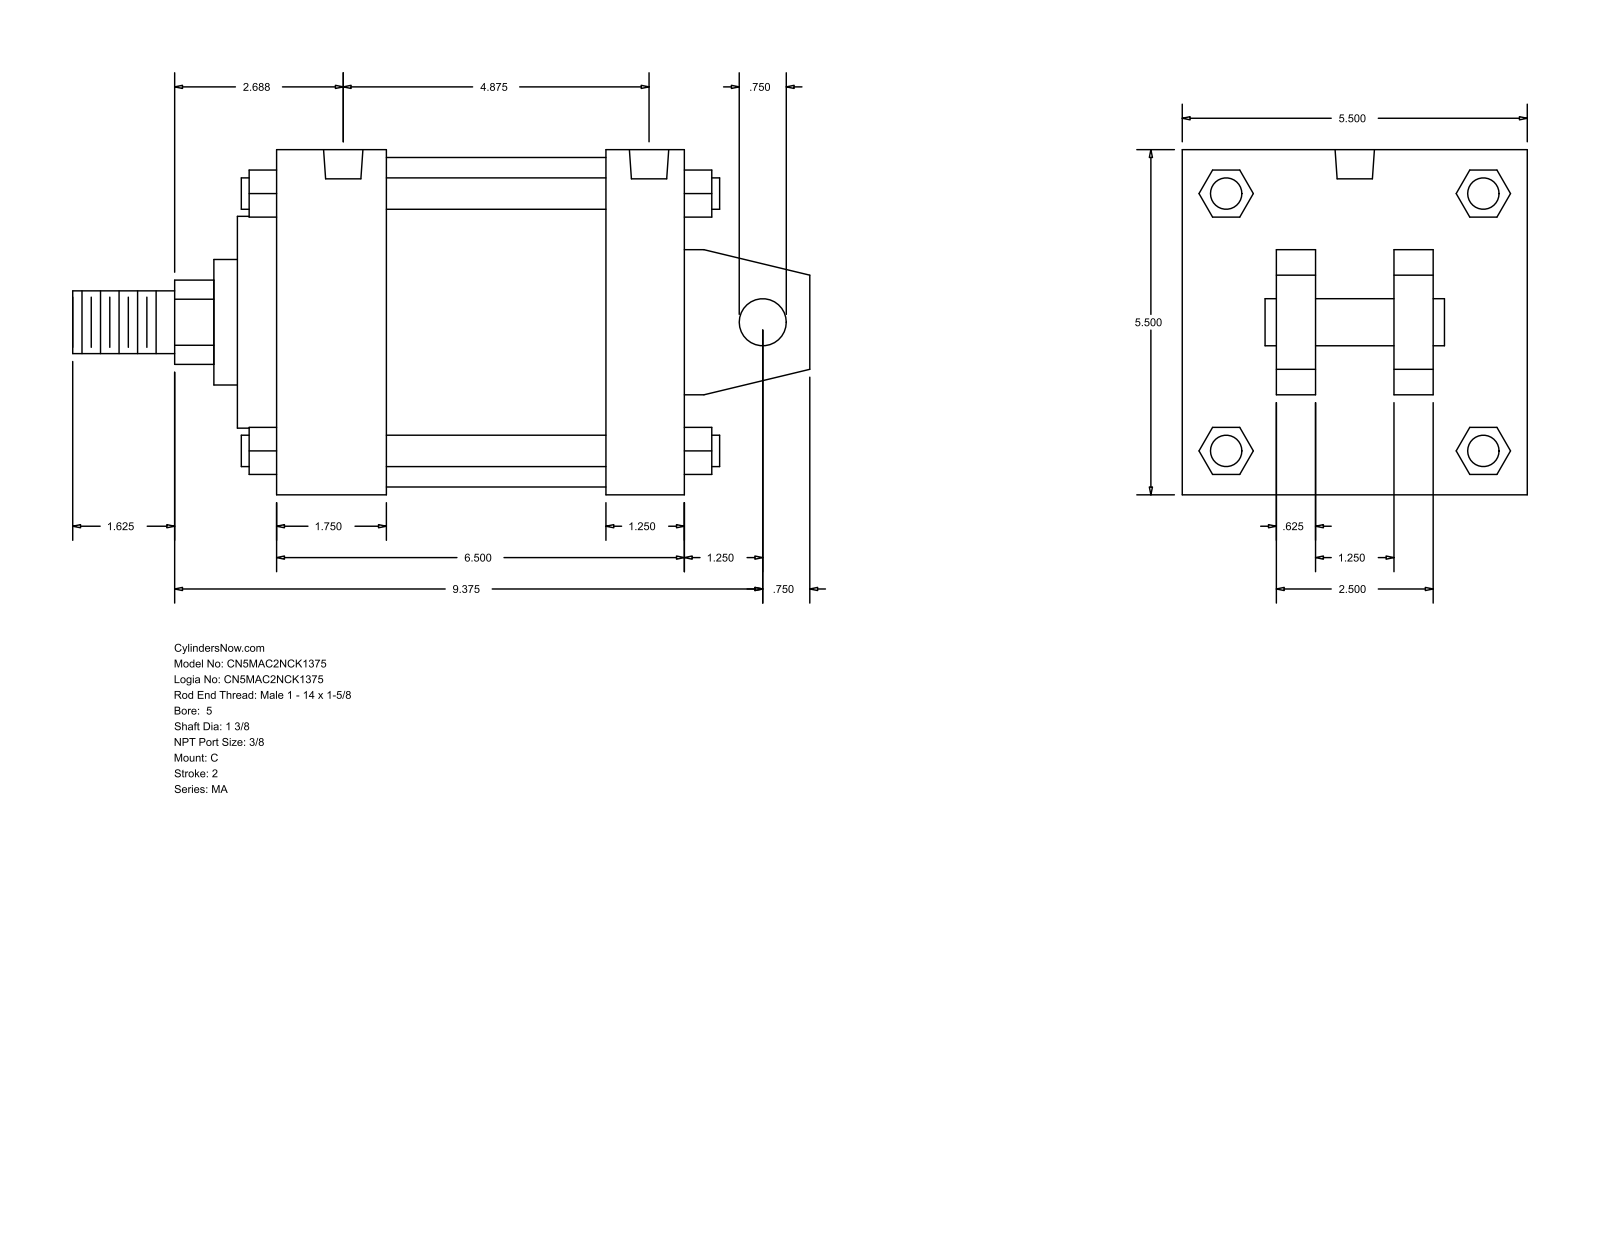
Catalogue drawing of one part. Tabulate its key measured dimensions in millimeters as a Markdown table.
| quantity | value |
| --- | --- |
| part name | MA_C__0500_1.375 |
| STEP written by | GSSL Pune (CONFIG_CONTROL_DESIGN) |
| units | millimeters |
| bodies | 0 solids, 141 faces (109 planar, 32 cylindrical, 0 other) |
| overall size | 298.45 × 139.7 × 139.7 |
| round holes (diameter × count) | 11.11 × 4, 15.93 × 2 |
| round bosses / shafts (diameter × count) | 12.7 × 4, 133.35 × 1, 85.72 × 1, 50.8 × 1, 34.92 × 1, 25.4 × 1, 19.05 × 1 |
| partial cylindrical surfaces (radius × count) | 17.06 × 1 |
| main face-to-face distances | 139.7, 165.11, 15.87, 31.76, 133.35, 44.45, 88.9, 120.66, 53.97, 38.1 |
| hole center spacings | 4.77, 114.29, 119.06, 123.83 |
